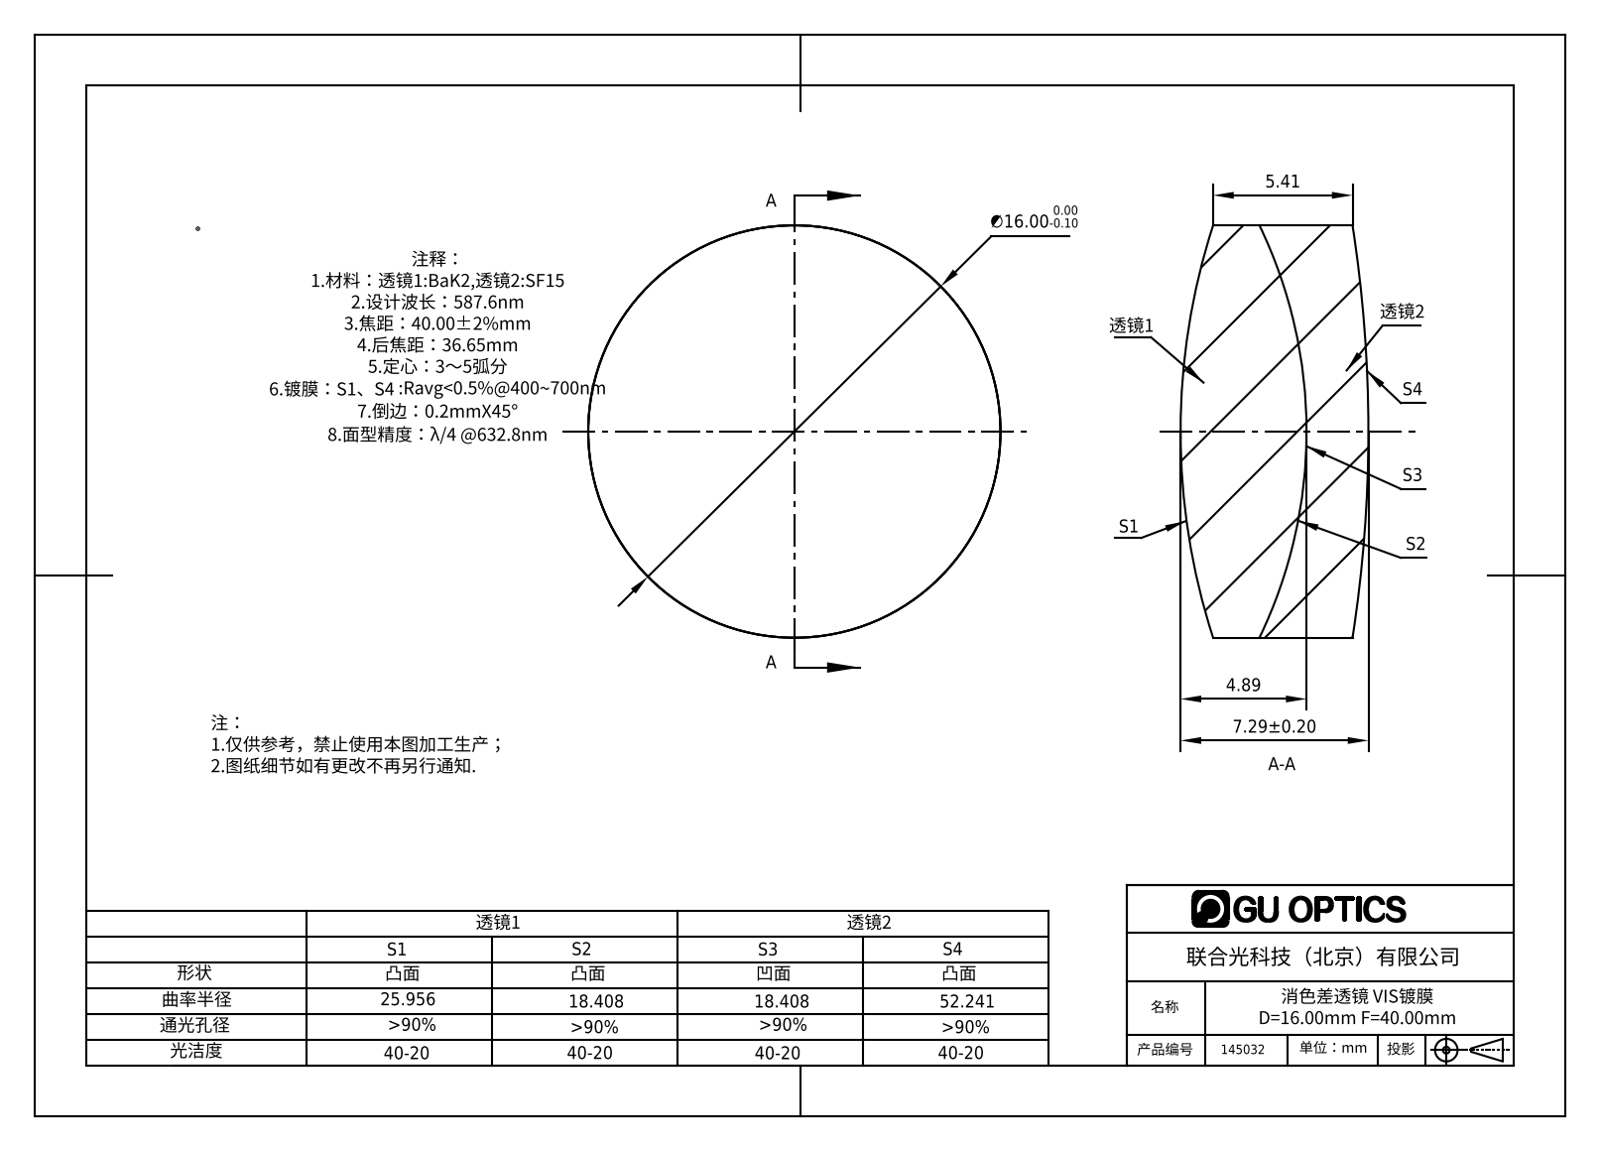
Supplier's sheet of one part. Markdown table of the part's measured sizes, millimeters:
| quantity | value |
| --- | --- |
| part name | 145032 |
| STEP written by | SolidWorks 2016 (AUTOMOTIVE_DESIGN) |
| units | millimeters |
| bodies | 2 solids, 12 faces (0 planar, 4 cylindrical, 8 other) |
| overall size | 16 × 16 × 7.29 |
| volume | 1 278 mm³ |
| surface area | 1 103 mm² |
| round bosses / shafts (diameter × count) | 16 × 1 |
